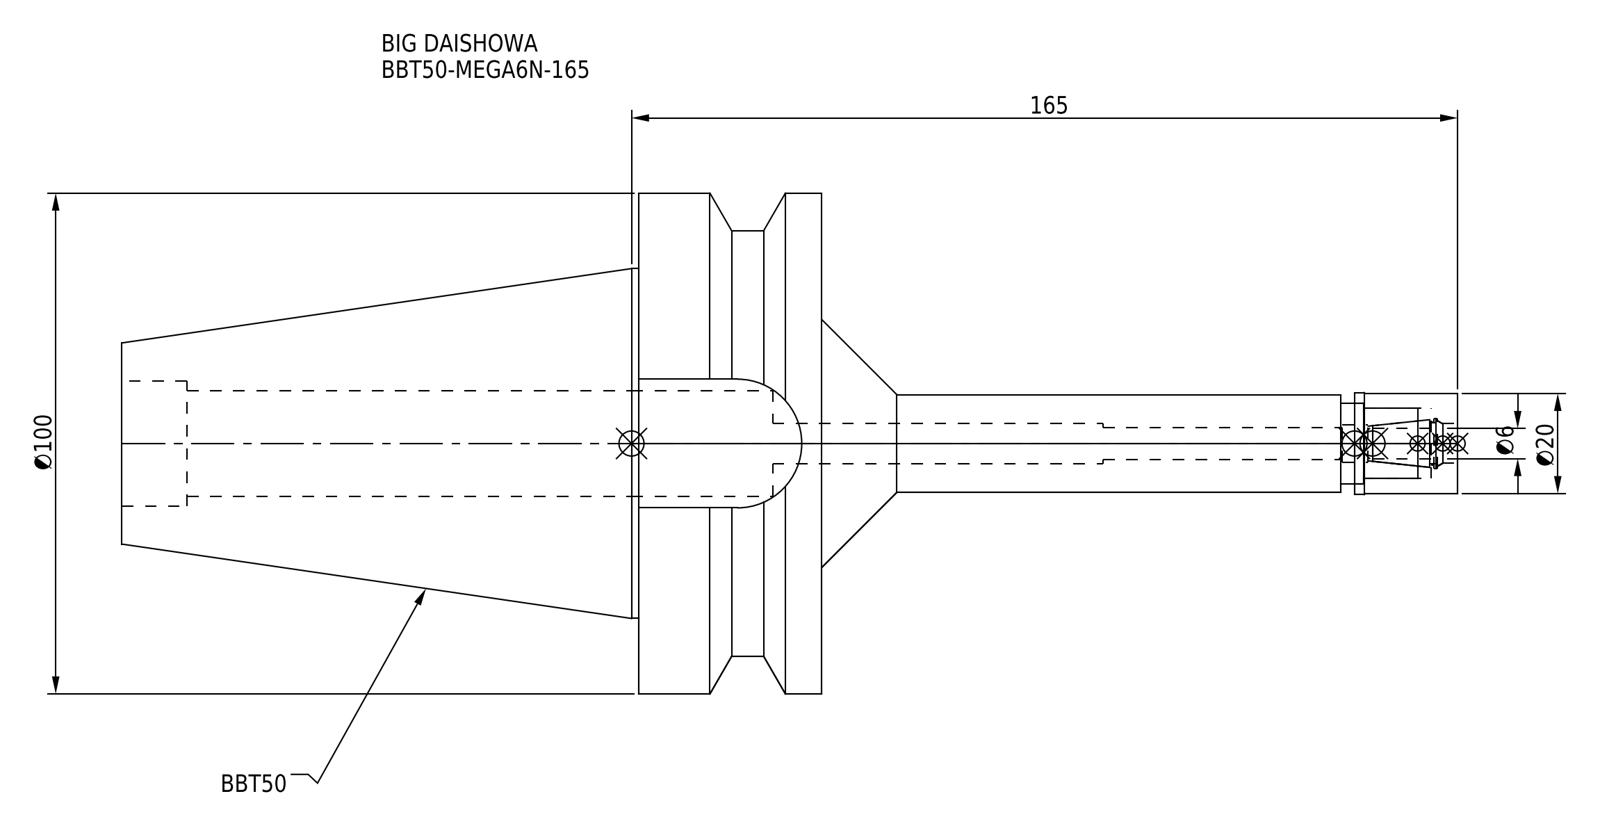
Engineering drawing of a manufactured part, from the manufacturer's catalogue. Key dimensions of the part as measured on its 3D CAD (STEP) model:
Part name (STEP PRODUCT): BBT50-MEGA6N-165-060-FreeParts; MGN6_1.stp; BBT50-MEGA6N-165; DXF_TEMP_ASSY_ASM_4_ASM.stp (+3 more)
STEP written by: SolidWorks 2019 (CONFIG_CONTROL_DESIGN)
Units: millimetres
Bodies: 2 solids, 79 faces (23 planar, 42 cylindrical, 14 other)
Overall size (bounding box): 266.8 × 100 × 100
Volume: 493 435 mm³ · Surface area: 66 584 mm²
Round holes (diameter × count): ⌀6.4 ×1, ⌀7.5 ×1, ⌀7.9 ×1, ⌀8 ×1, ⌀8.5 ×1, ⌀10 ×1, ⌀14 ×1, ⌀16 ×1, ⌀21.2 ×1, ⌀25 ×1
Round bosses / shafts (diameter × count): ⌀100 ×1, ⌀85 ×1, ⌀69.85 ×1, ⌀20.3 ×1, ⌀20 ×1, ⌀19.5 ×1
Partial cylindrical surfaces — rounded edges, fillets, slot ends (radius × count): R12.85 ×1
Main face-to-face distances: 36.5, 70.8, 139.8, 103.3, 25.7, 9.8, 26.7, 130, 127, 136.8
